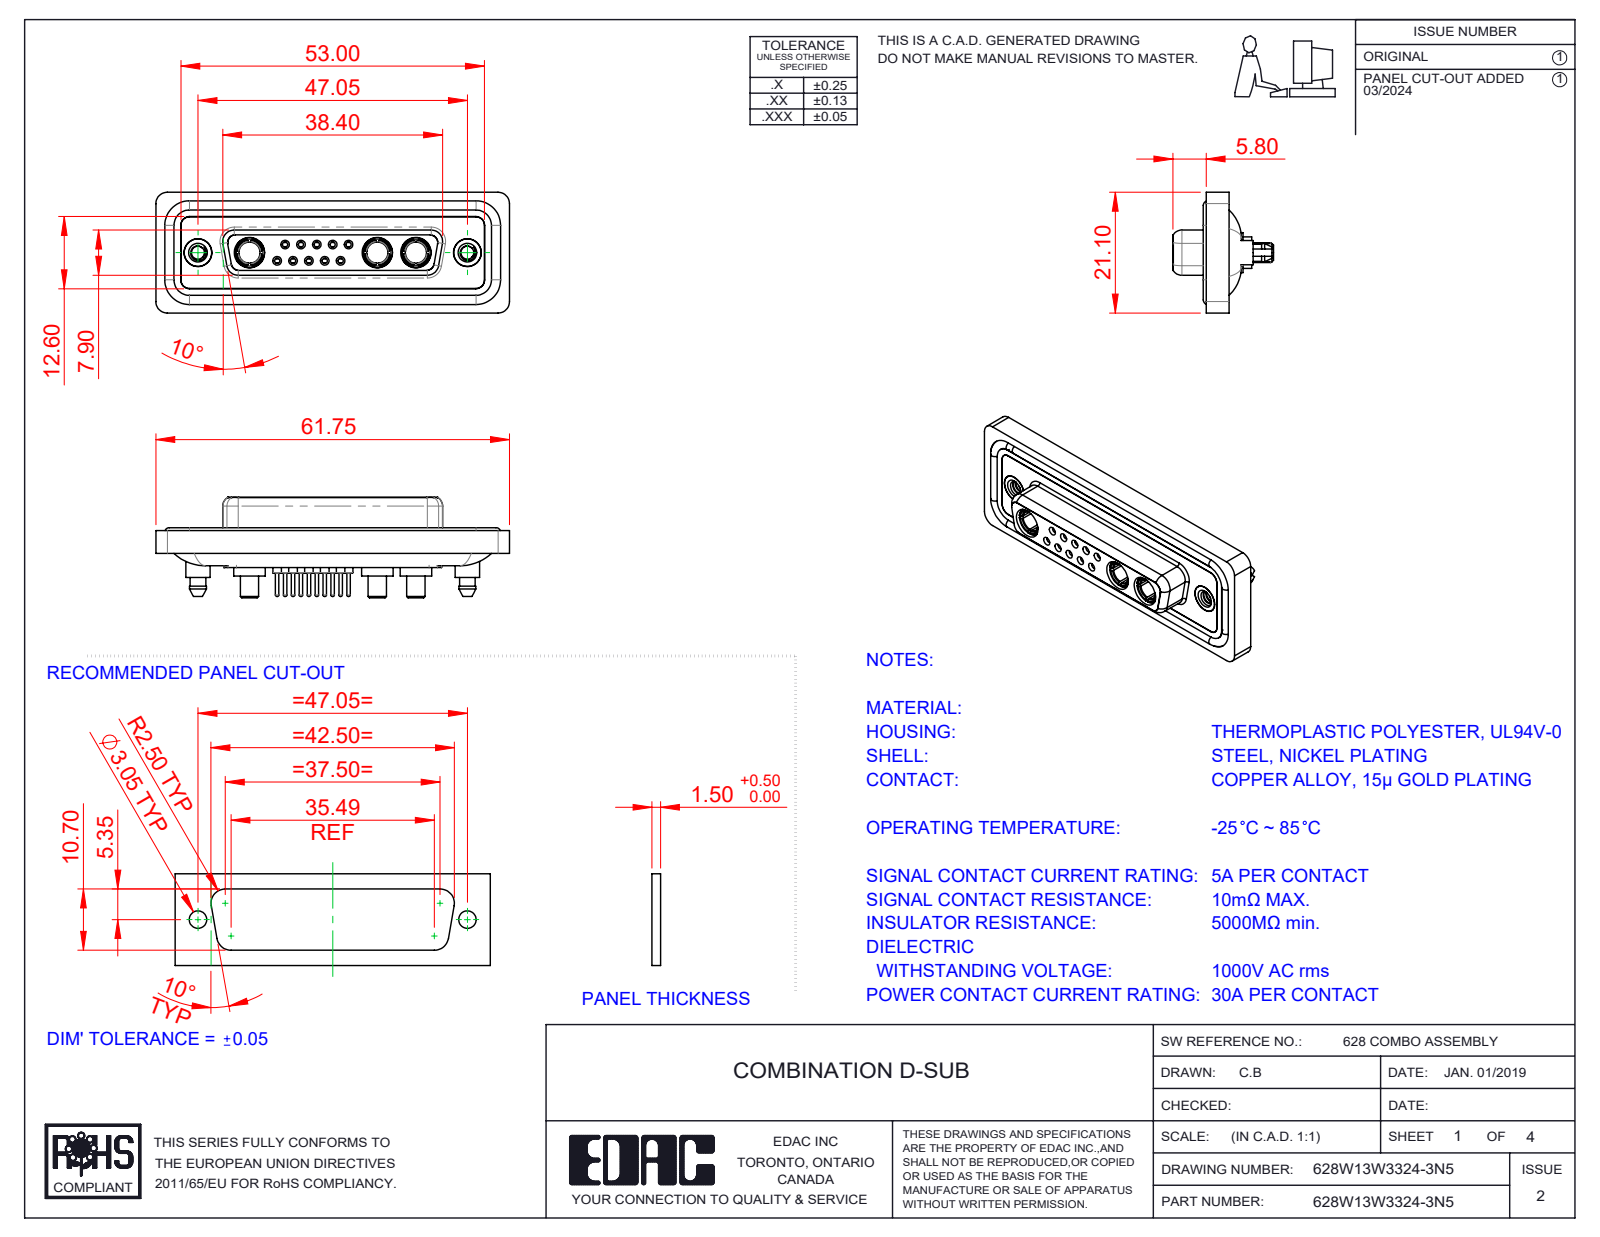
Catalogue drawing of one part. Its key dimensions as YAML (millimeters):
part_name: "628Combo Shell Front_25 Contacts; 628Combo Waterproof Housing_25 Contacts; 628Combo Contact Row 1_24; 628Combo Shell Rear_25 Contacts (+5 more)"
step_written_by: "SolidWorks 2023 (CONFIG_CONTROL_DESIGN)"
units: millimeters
bodies: {solids: 23, faces: 1208, planar: 358, cylindrical: 479, other: 371}
overall_size: [61.75, 21.1, 17.55]
volume: 8428
surface_area: 14055
round_holes:
  - {diameter: 0.9, count: 10}
  - {diameter: 1.1, count: 10}
  - {diameter: 1.5, count: 10}
  - {diameter: 2, count: 10}
  - {diameter: 1.6, count: 5}
  - {diameter: 1.7, count: 5}
  - {diameter: 4.85, count: 5}
  - {diameter: 3.7, count: 3}
  - {diameter: 5.3, count: 3}
  - {diameter: 2.26, count: 2}
  - {diameter: 4, count: 2}
  - {diameter: 4.05, count: 2}
round_bosses_or_shafts:
  - {diameter: 2.2, count: 10}
  - {diameter: 0.6, count: 10}
  - {diameter: 1.6, count: 9}
  - {diameter: 5.5, count: 3}
  - {diameter: 5.2, count: 3}
  - {diameter: 4.96, count: 3}
  - {diameter: 4.75, count: 3}
  - {diameter: 3.75, count: 3}
partial_cylinders:
  - {radius: 1.5, count: 24}
  - {radius: 2, count: 18}
  - {radius: 1.6, count: 10}
  - {radius: 1.35, count: 8}
  - {radius: 0.25, count: 4}
  - {radius: 0.5, count: 4}
  - {radius: 0.6, count: 4}
  - {radius: 0.65, count: 4}
face_to_face_distances: [0.4, 1.8, 7.45, 5.65, 0.5, 6.6, 7.05, 1.6, 2.9, 1.1]
hole_center_spacings: [3.16, 2.77, 5.03, 5.04, 5.54, 8.31, 7.49, 2.76]
